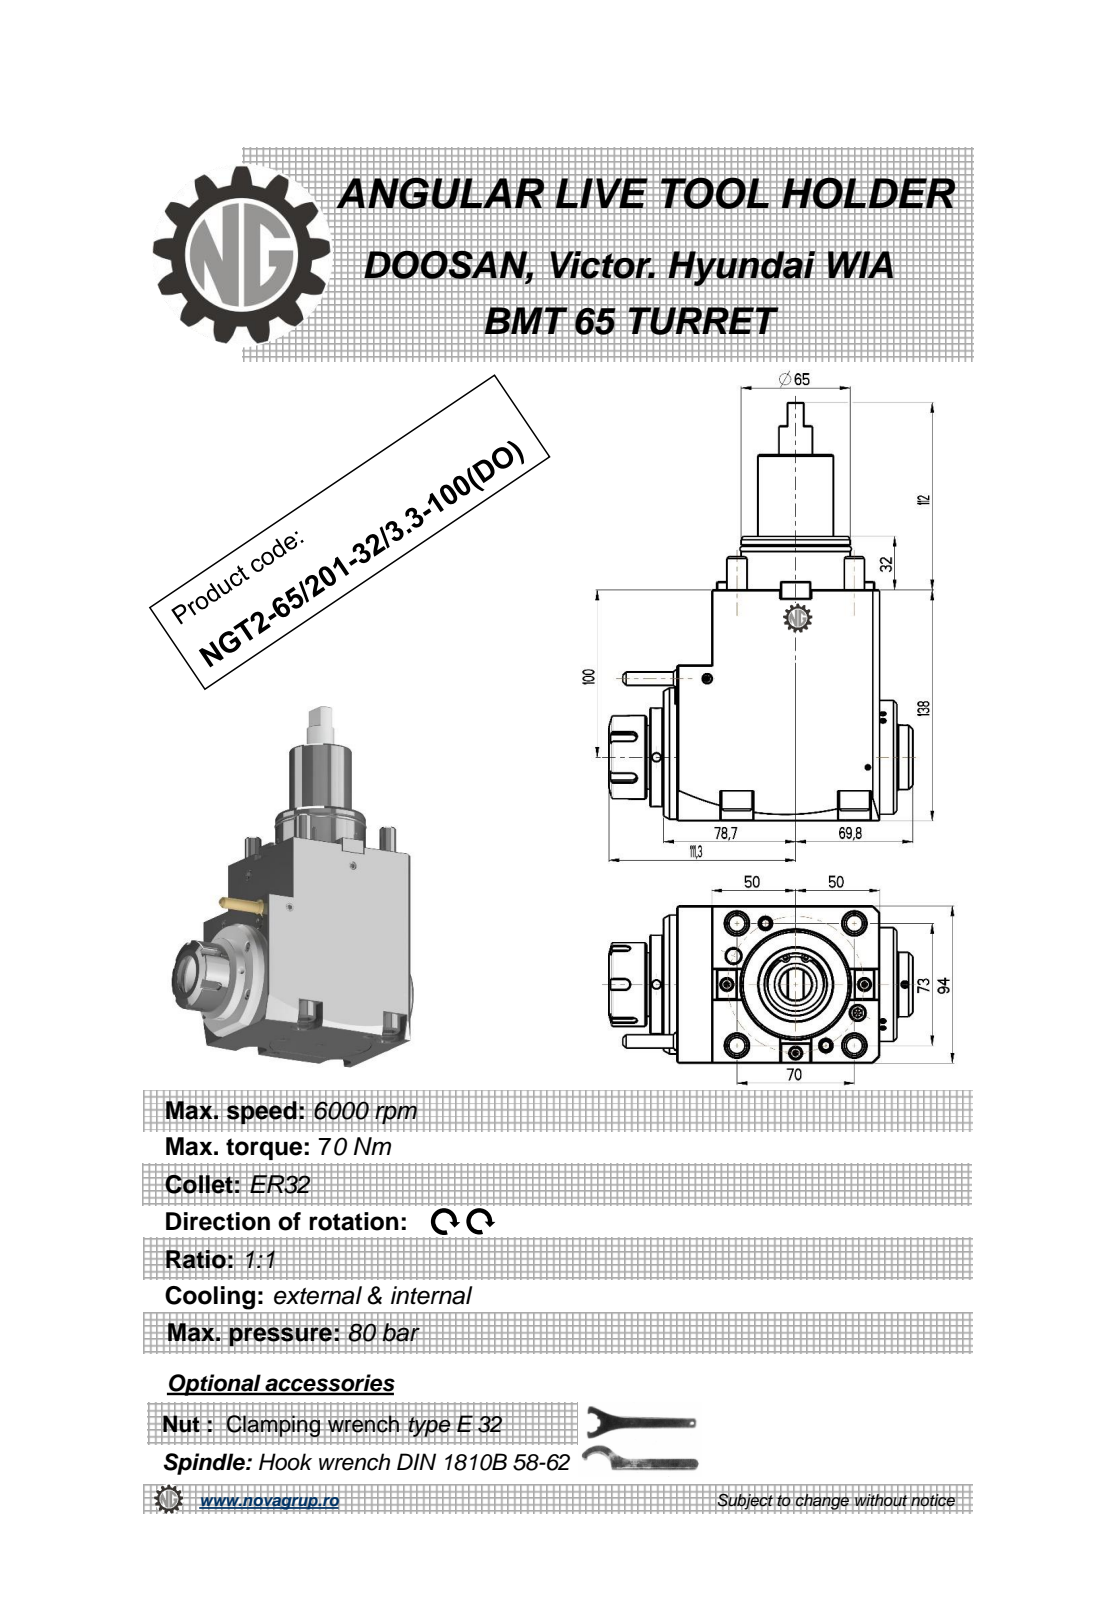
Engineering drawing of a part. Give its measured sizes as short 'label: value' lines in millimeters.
name: NGT2_65_201_32_3_3_100_DO
written by: PRO/ENGINEER BY PARAMETRIC TECHNOLOGY CORPORATION, 2010280 (CONFIG_CONTROL_DESIGN)
unit: mm
bodies: 2 solids, 445 faces (217 planar, 112 cylindrical, 116 other)
size: 250 × 181.1 × 94
volume: 1 812 000 mm³; area: 122 845 mm²
holes: 3× ⌀5, 2× ⌀8.5, 1× ⌀3, 1× ⌀27
bosses: 4× ⌀18, 4× ⌀12, 1× ⌀83, 1× ⌀68, 1× ⌀65, 1× ⌀60, 1× ⌀59, 1× ⌀50
rounds: 20× R0.36, 6× R0.22, 5× R3, 4× R9.5, 2× R0.8, 2× R550
face distances: 94, 138, 8, 100, 28.7, 128.7, 20.7, 120.7, 45, 93
hole spacings: 48.99, 58.01, 81.44, 121.15
